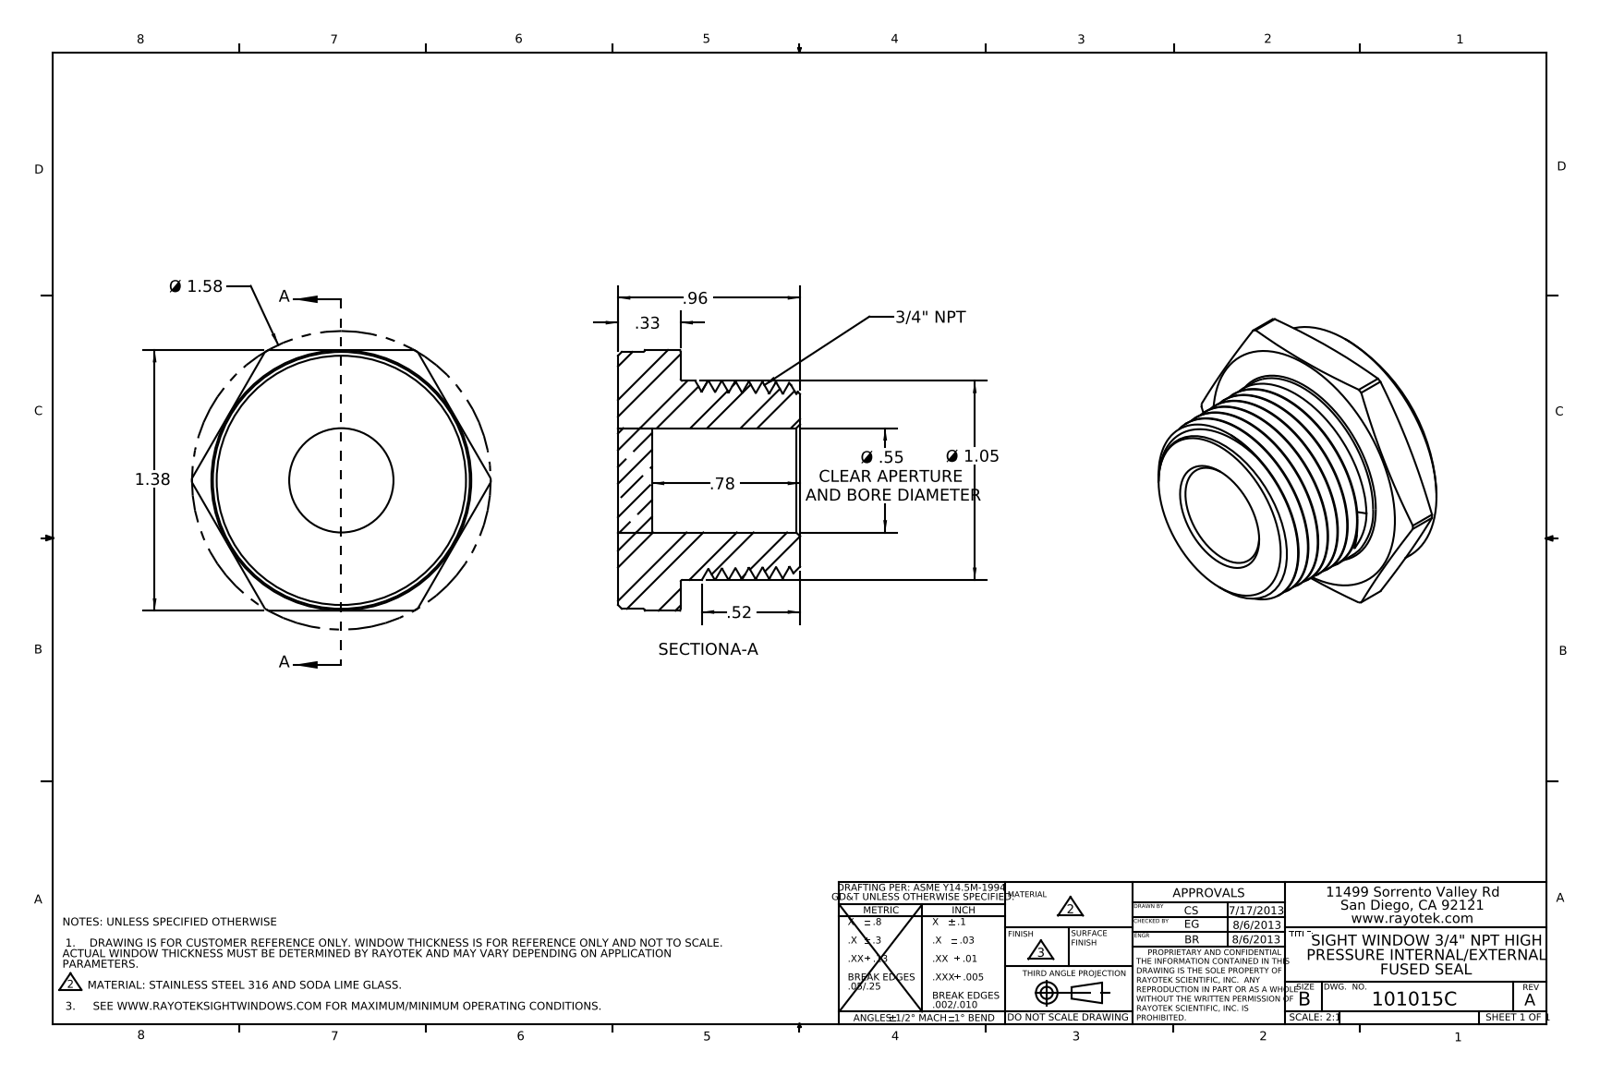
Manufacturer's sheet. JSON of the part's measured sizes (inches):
{"part_name": "101015; 402015; 403015_CUSTOMER", "step_written_by": "SolidWorks 2012 (AUTOMOTIVE_DESIGN)", "units": "inches", "bodies": {"solids": 2, "faces": 61, "planar": 14, "cylindrical": 15, "other": 32}, "overall_size": [1.576, 1.375, 0.96], "volume_in3": 0.81, "surface_area_in2": 9.765, "round_holes": [[0.55, 1]], "round_bosses_or_shafts": [[1.355, 1], [1.05, 1]], "partial_cylinders_radius": [[0.788, 1]], "face_to_face_distances": [0.33, 1.375, 0.96, 0.63, 0.179, 0.151, 0.781]}
